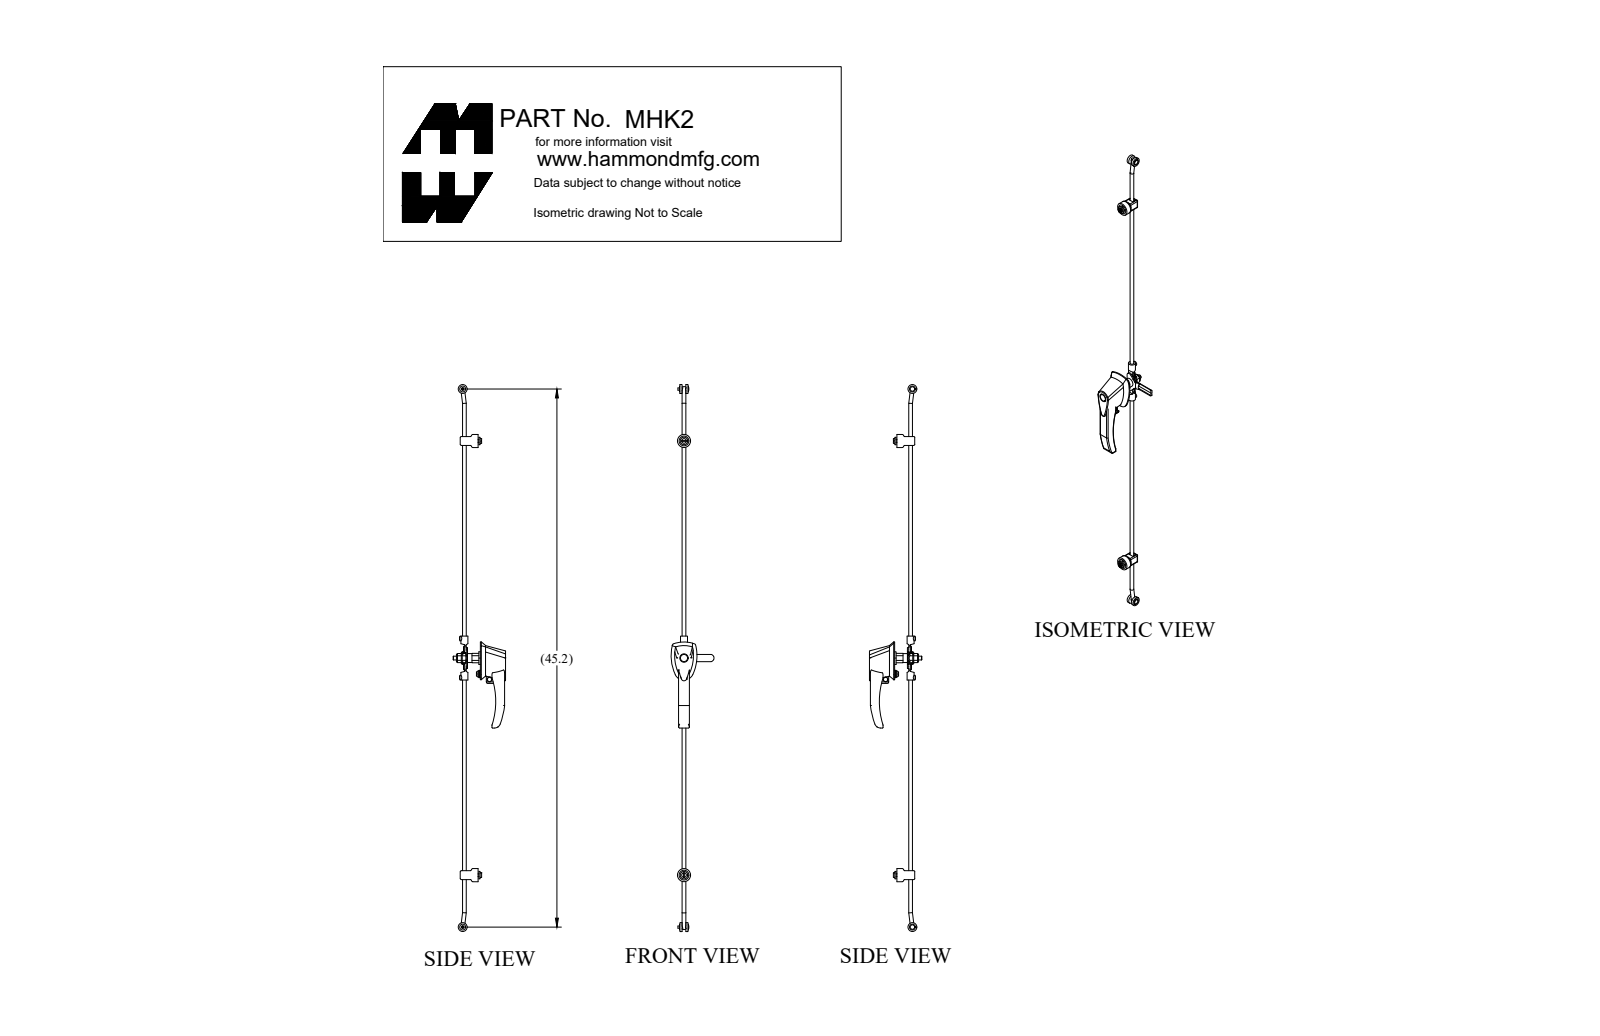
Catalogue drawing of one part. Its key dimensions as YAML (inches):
part_name: "MHK2"
step_written_by: "SolidWorks 2018 (AUTOMOTIVE_DESIGN)"
units: inches
bodies: {solids: 30, faces: 533, planar: 233, cylindrical: 211, other: 89}
overall_size: [45.911, 4.398, 3.607]
volume: 16.74
surface_area: 139.6
round_holes:
  - {diameter: 0.127, count: 2}
  - {diameter: 0.187, count: 2}
  - {diameter: 0.189, count: 2}
  - {diameter: 0.218, count: 2}
  - {diameter: 0.236, count: 2}
  - {diameter: 0.25, count: 2}
  - {diameter: 0.827, count: 2}
  - {diameter: 0.233, count: 1}
  - {diameter: 0.275, count: 1}
  - {diameter: 0.275, count: 1}
  - {diameter: 0.325, count: 1}
  - {diameter: 0.335, count: 1}
round_bosses_or_shafts:
  - {diameter: 0.75, count: 3}
  - {diameter: 0.313, count: 3}
  - {diameter: 1.102, count: 2}
  - {diameter: 0.5, count: 2}
  - {diameter: 0.394, count: 2}
  - {diameter: 0.375, count: 2}
  - {diameter: 0.224, count: 2}
  - {diameter: 0.187, count: 2}
partial_cylinders:
  - {radius: 0.09, count: 20}
  - {radius: 0.03, count: 6}
  - {radius: 0.06, count: 5}
  - {radius: 0.036, count: 4}
  - {radius: 0.108, count: 4}
  - {radius: 0.125, count: 3}
  - {radius: 0.25, count: 3}
  - {radius: 0.22, count: 2}
face_to_face_distances: [0.91, 0.114, 0.796, 2.115, 0.081, 0.829, 0.033, 0.715, 0.299, 0.611]
hole_center_spacings: [0.687, 17.532, 18.22, 18.907, 0.651, 1.338, 1.375, 2.026]
